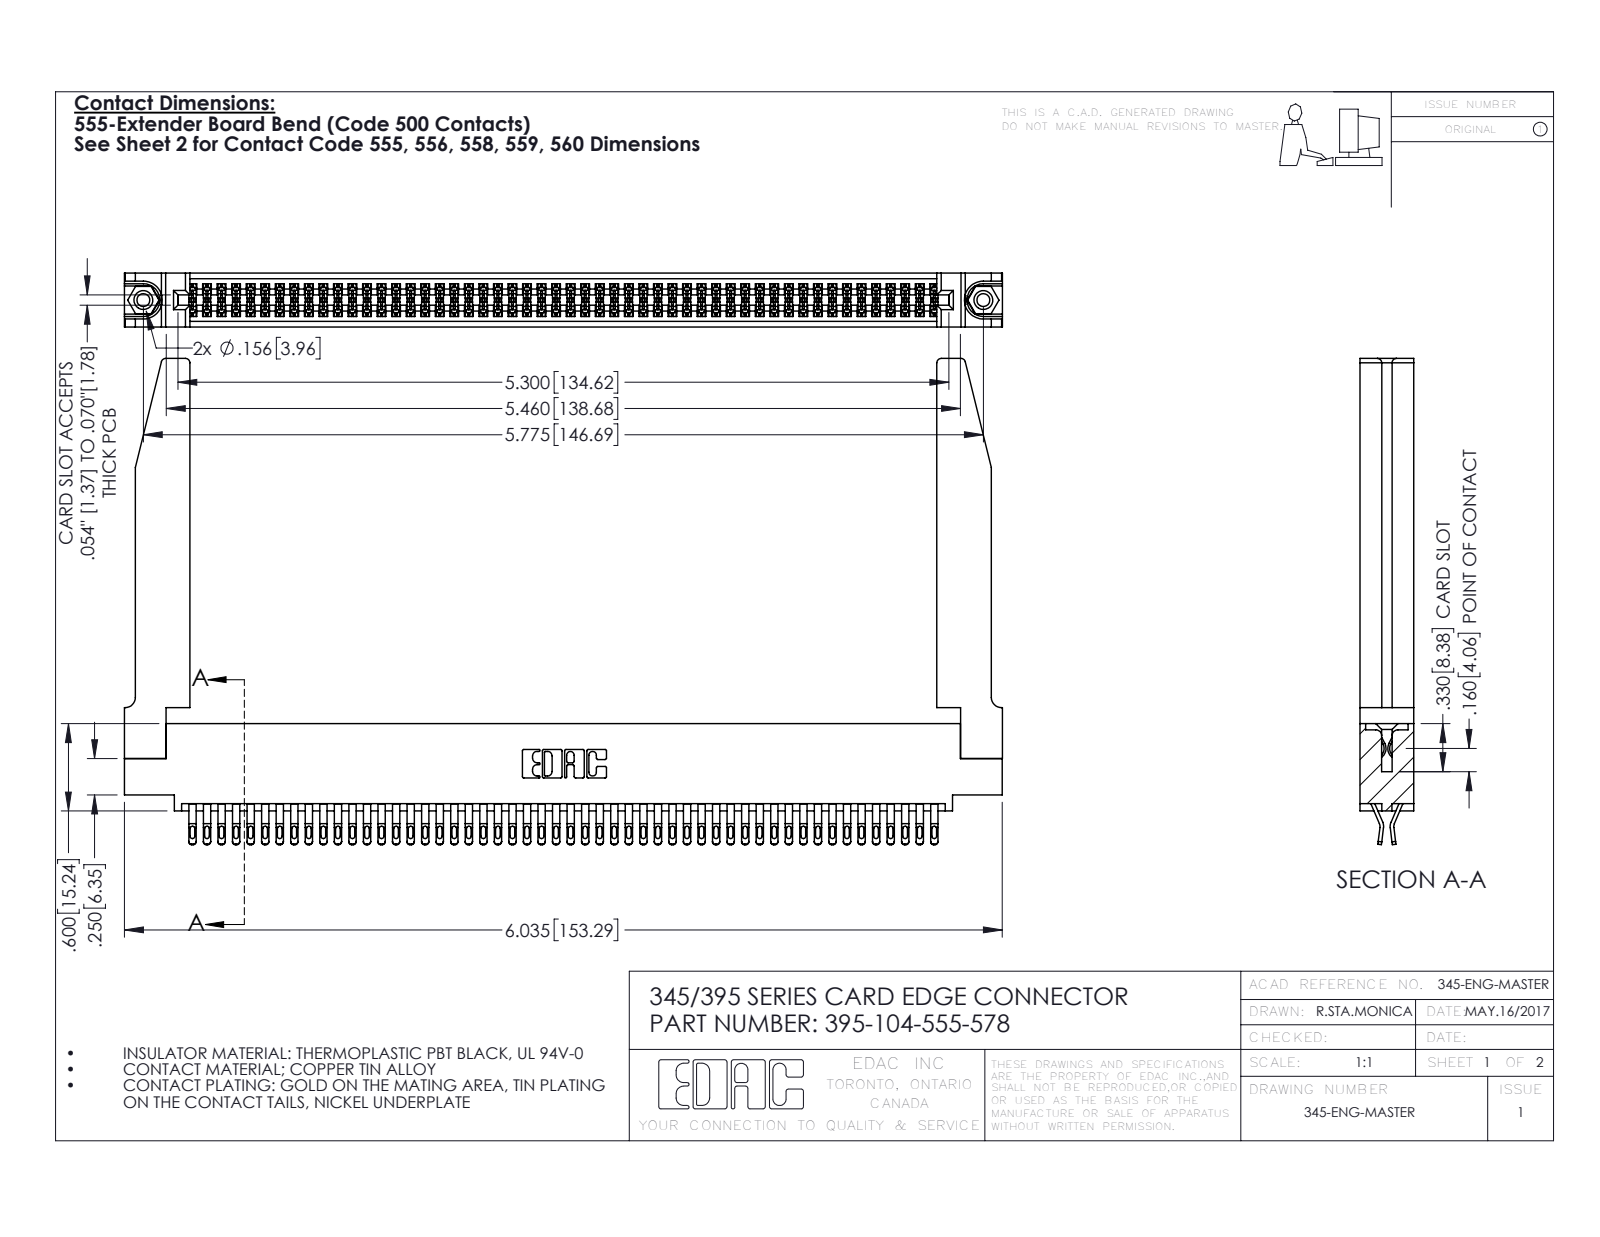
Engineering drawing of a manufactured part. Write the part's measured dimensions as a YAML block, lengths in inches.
part_name: "395-104-555-578; 345 Part_0.110 Offset - 0.156 Dia-TH; 345-220-078_345-220-078; 345-250-001_345-250-001-102 (+1 more)"
step_written_by: "SolidWorks 2016 (CONFIG_CONTROL_DESIGN)"
units: inches
bodies: {solids: 109, faces: 6188, planar: 3450, cylindrical: 2686, other: 52}
overall_size: [6.036, 3.342, 0.37]
volume: 1.403
surface_area: 47.53
round_holes:
  - {diameter: 0.089, count: 2}
  - {diameter: 0.125, count: 2}
  - {diameter: 0.156, count: 2}
  - {diameter: 0.064, count: 1}
round_bosses_or_shafts:
  - {diameter: 0.155, count: 2}
partial_cylinders:
  - {radius: 0.016, count: 260}
  - {radius: 0.02, count: 208}
  - {radius: 0.006, count: 156}
  - {radius: 0.01, count: 22}
  - {radius: 0.03, count: 8}
  - {radius: 0.007, count: 6}
  - {radius: 0.031, count: 6}
  - {radius: 0.026, count: 3}
face_to_face_distances: [0.072, 0.37, 0.298, 0.025, 0.098, 0.272, 0.2, 0.225, 0.175, 0.15]
hole_center_spacings: [0.27, 5.539, 5.775]
